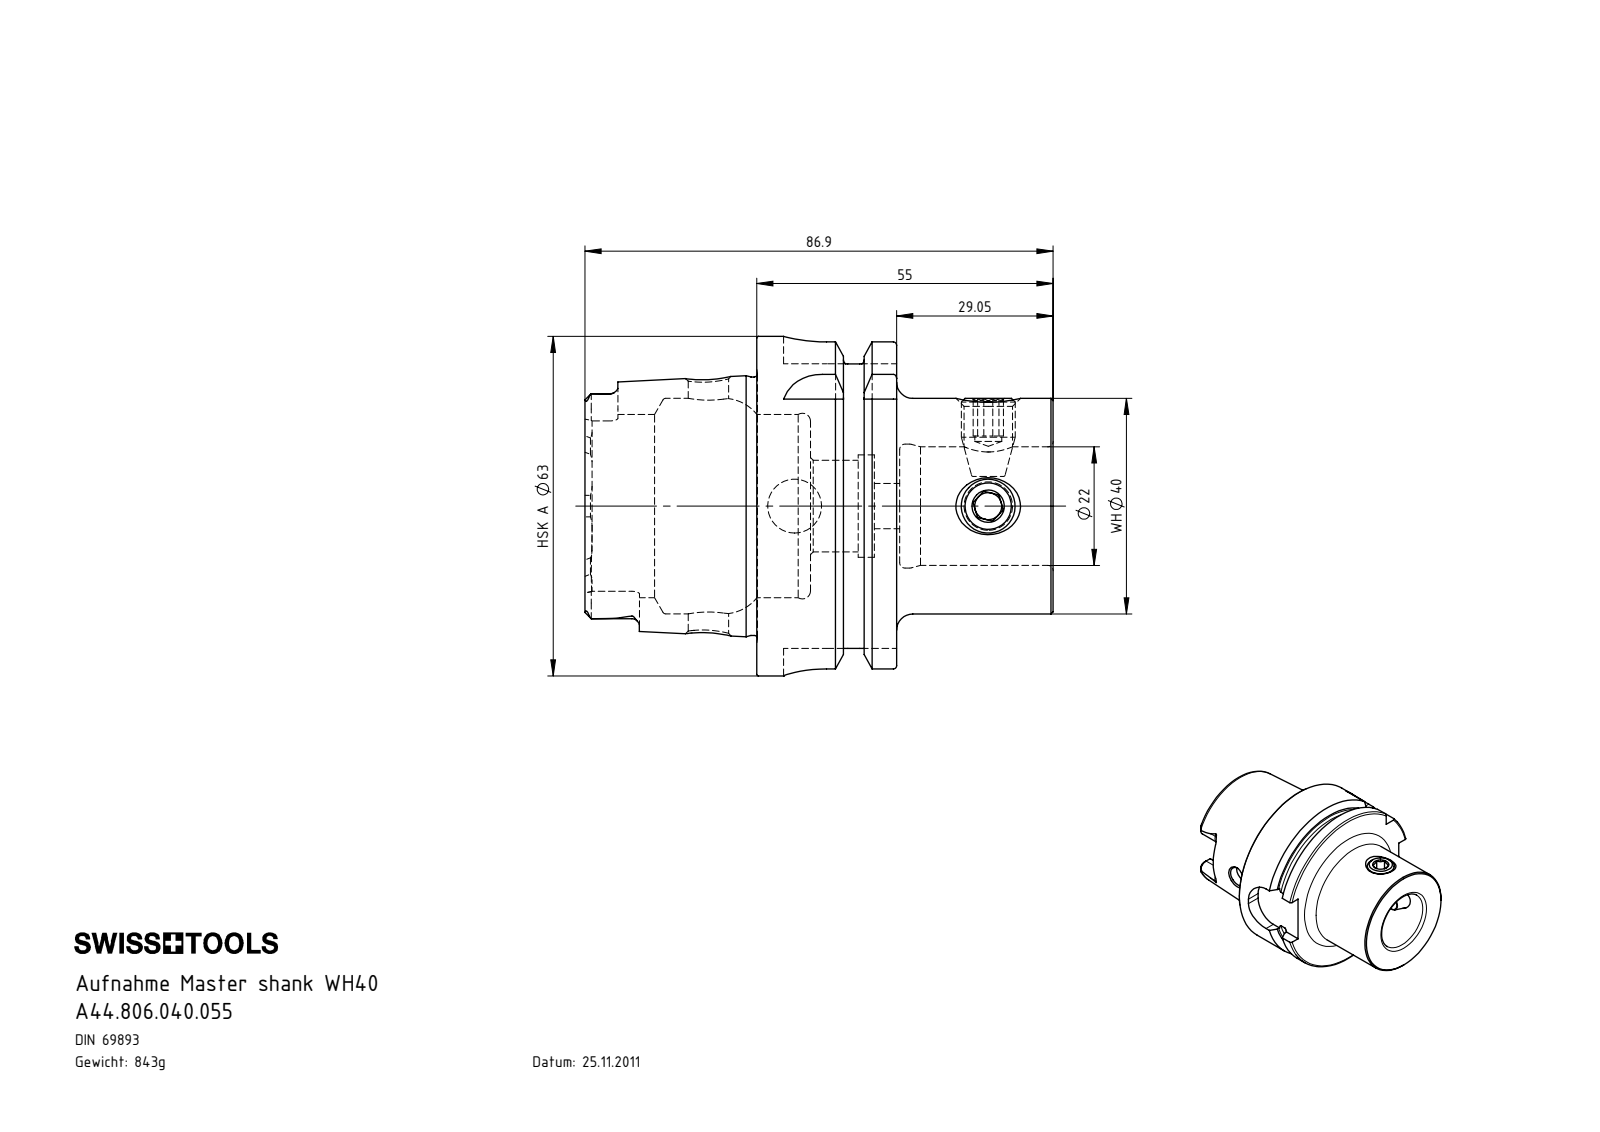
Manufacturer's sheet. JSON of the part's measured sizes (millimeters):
{"part_name": "HA6-WH4.K01.055_B; WH4-ER1.001.015; HA6.WH4.K01.055", "step_written_by": "SolidWorks 2017 (AUTOMOTIVE_DESIGN)", "units": "millimeters", "bodies": {"solids": 3, "faces": 183, "planar": 75, "cylindrical": 39, "other": 69}, "overall_size": [86.9, 63, 63], "volume_mm3": 107358, "surface_area_mm2": 29166, "round_holes": [[5, 2], [9, 2], [7.5, 1], [8.4, 1], [10, 1], [17, 1], [19, 1], [22, 1], [23, 1], [34, 1], [40, 1]], "round_bosses_or_shafts": [[10, 2], [63, 1], [54.95, 1], [47.94, 1]], "partial_cylinders_radius": [[1.4, 6], [2.88, 4], [8, 4]], "face_to_face_distances": [25.95, 55, 29.05, 16, 9.95, 45.05, 31.9, 41.85, 57.85, 86.9], "hole_center_spacings": [35.95, 51.95]}
